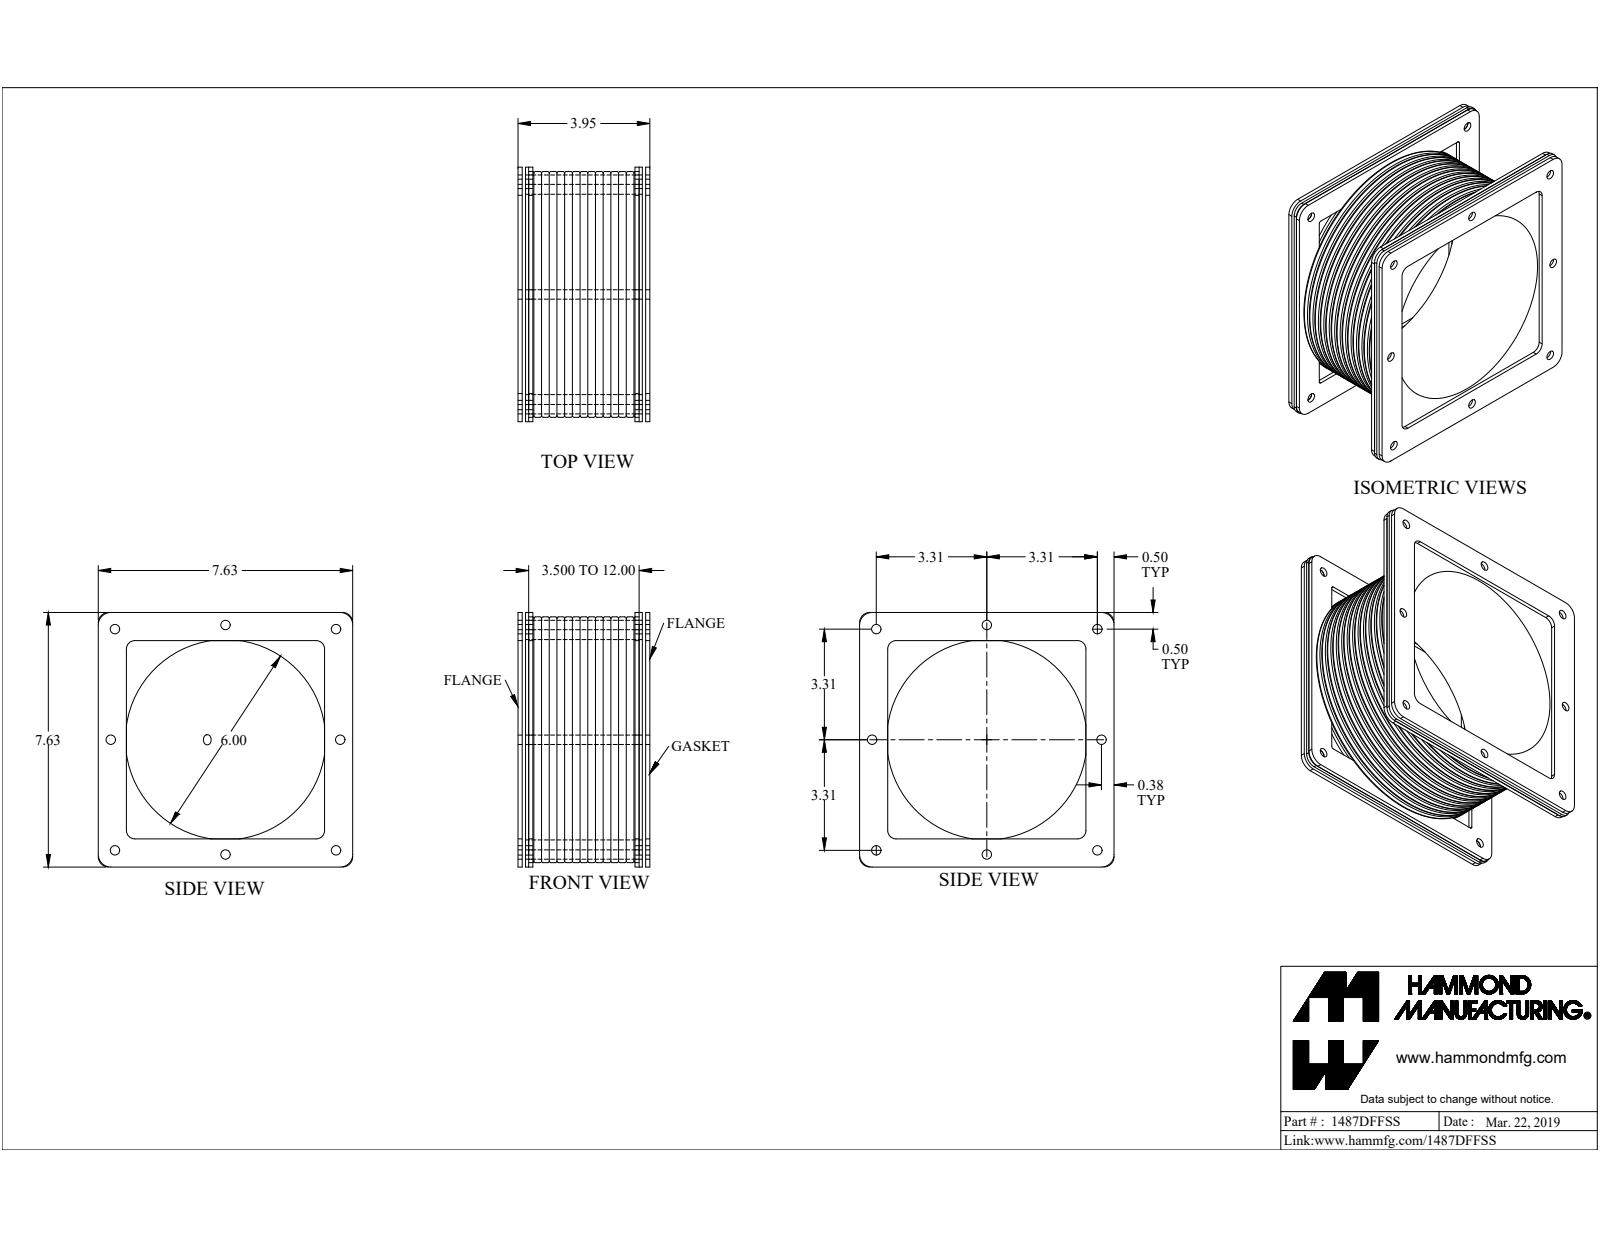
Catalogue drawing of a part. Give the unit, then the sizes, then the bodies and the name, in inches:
Units: inches
Overall size (bounding box): 7.625 × 7.625 × 4.501
Round holes (diameter × count): ⌀0.281 ×8, ⌀0.281 ×8, ⌀0.196 ×1, ⌀0.258 ×1, ⌀0.35 ×1, ⌀6 ×1
Round bosses / shafts (diameter × count): ⌀7.362 ×1, ⌀0.5 ×1, ⌀0.25 ×1
Partial cylindrical surfaces — rounded edges, fillets, slot ends (radius × count): R0.02 ×12, R0.063 ×4, R0.25 ×4, R0.313 ×4, R0.375 ×4
Main face-to-face distances: 0.095, 3.405, 0.22, 3.28, 0.125, 3.185, 0.225, 0.32, 0.445, 3.505
Hole centre spacings: 3.315, 7.519, 3.437, 4.685, 4.861, 6.625, 6.875, 9.369
Volume: 63 in³ · Surface area: 481.6 in²
Bodies: 11 solids, 354 faces (166 planar, 144 cylindrical, 44 other)
Part name (STEP PRODUCT): 1487DFFSS
STEP written by: SolidWorks 2019 (CONFIG_CONTROL_DESIGN)
